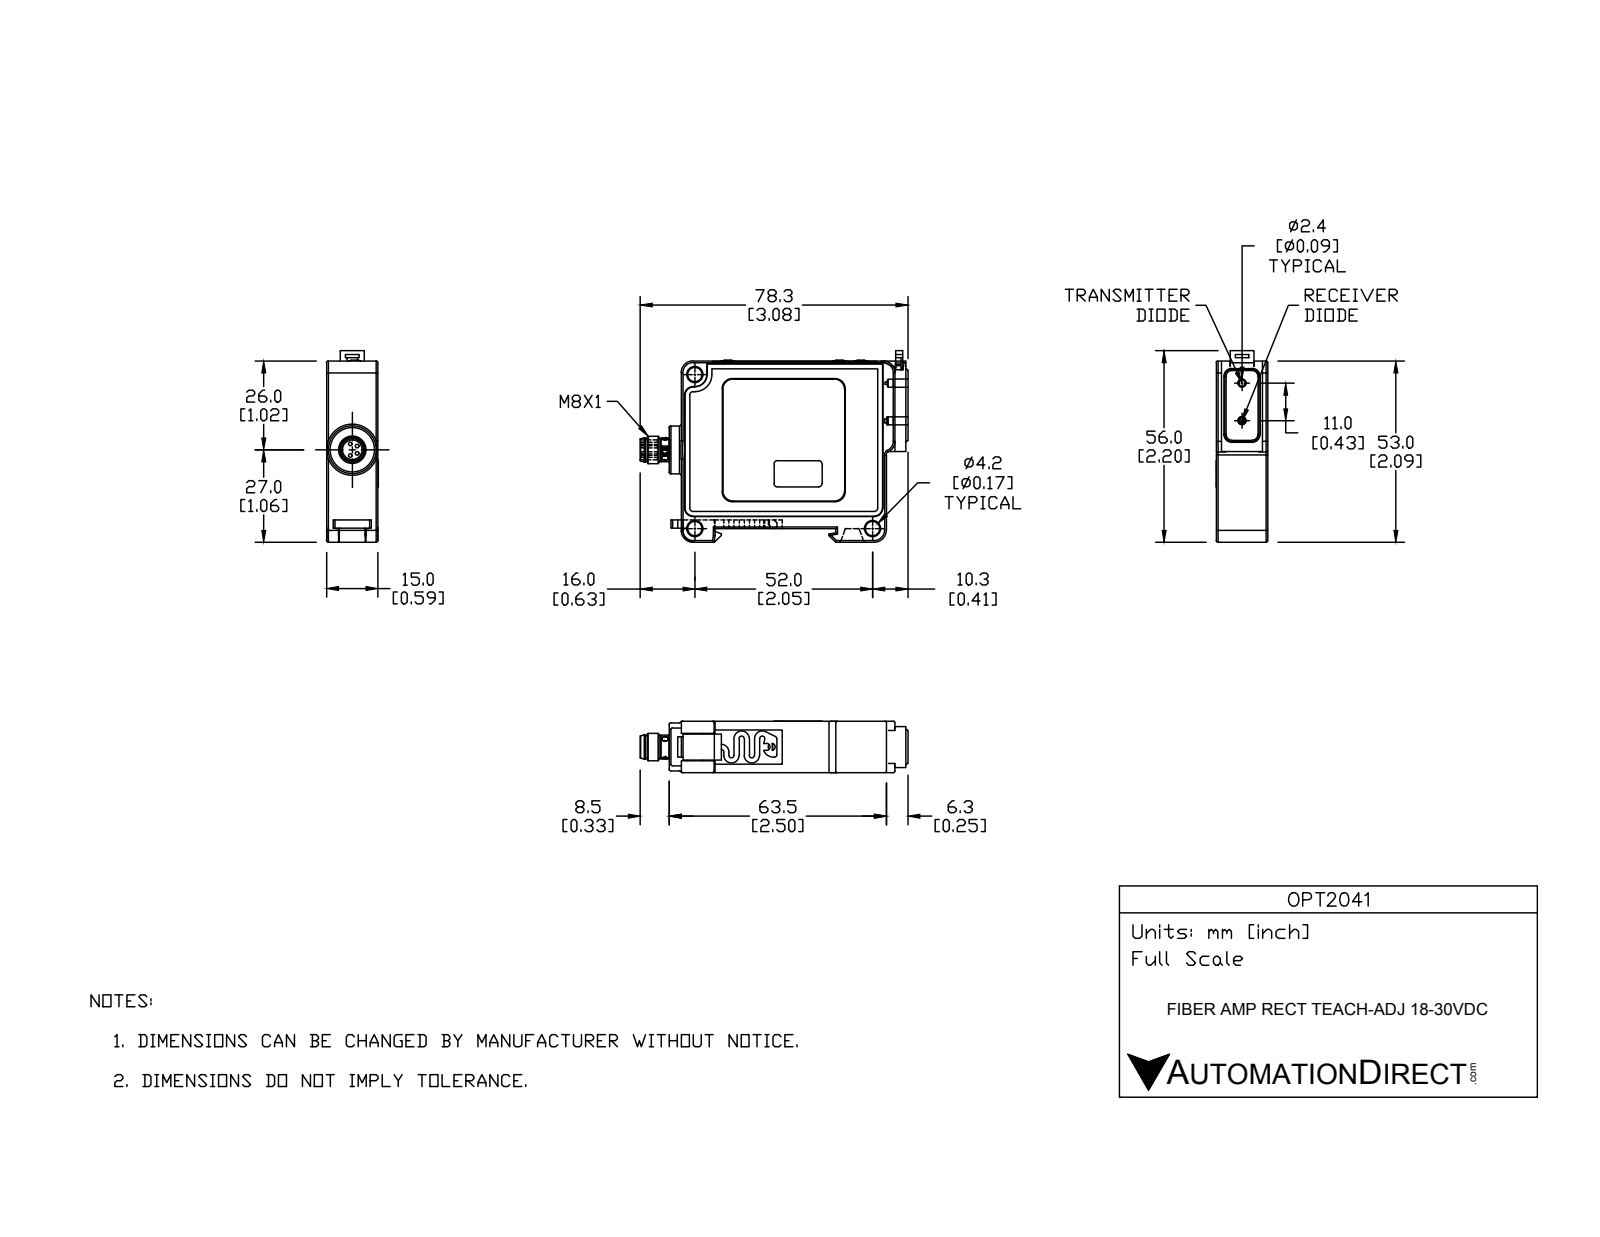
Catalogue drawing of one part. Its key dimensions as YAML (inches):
part_name: "OPT2041"
step_written_by: "SolidWorks 2014 (AUTOMOTIVE_DESIGN)"
units: inches
bodies: {solids: 1, faces: 659, planar: 307, cylindrical: 205, other: 147}
overall_size: [3.083, 2.205, 0.594]
volume: 2.86
surface_area: 18.82
round_holes:
  - {diameter: 0.075, count: 3}
  - {diameter: 0.165, count: 3}
  - {diameter: 0.071, count: 2}
  - {diameter: 0.091, count: 2}
  - {diameter: 0.094, count: 2}
  - {diameter: 0.047, count: 1}
  - {diameter: 0.079, count: 1}
  - {diameter: 0.173, count: 1}
  - {diameter: 0.228, count: 1}
round_bosses_or_shafts:
  - {diameter: 0.039, count: 4}
  - {diameter: 0.157, count: 3}
  - {diameter: 0.551, count: 1}
  - {diameter: 0.315, count: 1}
  - {diameter: 0.283, count: 1}
  - {diameter: 0.272, count: 1}
  - {diameter: 0.26, count: 1}
  - {diameter: 0.252, count: 1}
partial_cylinders:
  - {radius: 0.02, count: 24}
  - {radius: 0.016, count: 12}
  - {radius: 0.039, count: 10}
  - {radius: 0.03, count: 9}
  - {radius: 0.118, count: 9}
  - {radius: 0.012, count: 8}
  - {radius: 0.138, count: 7}
  - {radius: 0.089, count: 5}
face_to_face_distances: [0.586, 0.582, 0.59, 1.925, 0.591, 0.587, 0.098, 1.929, 2.362, 0.157]
hole_center_spacings: [0.335, 0.433, 0.768, 1.772, 2.047, 2.707]
